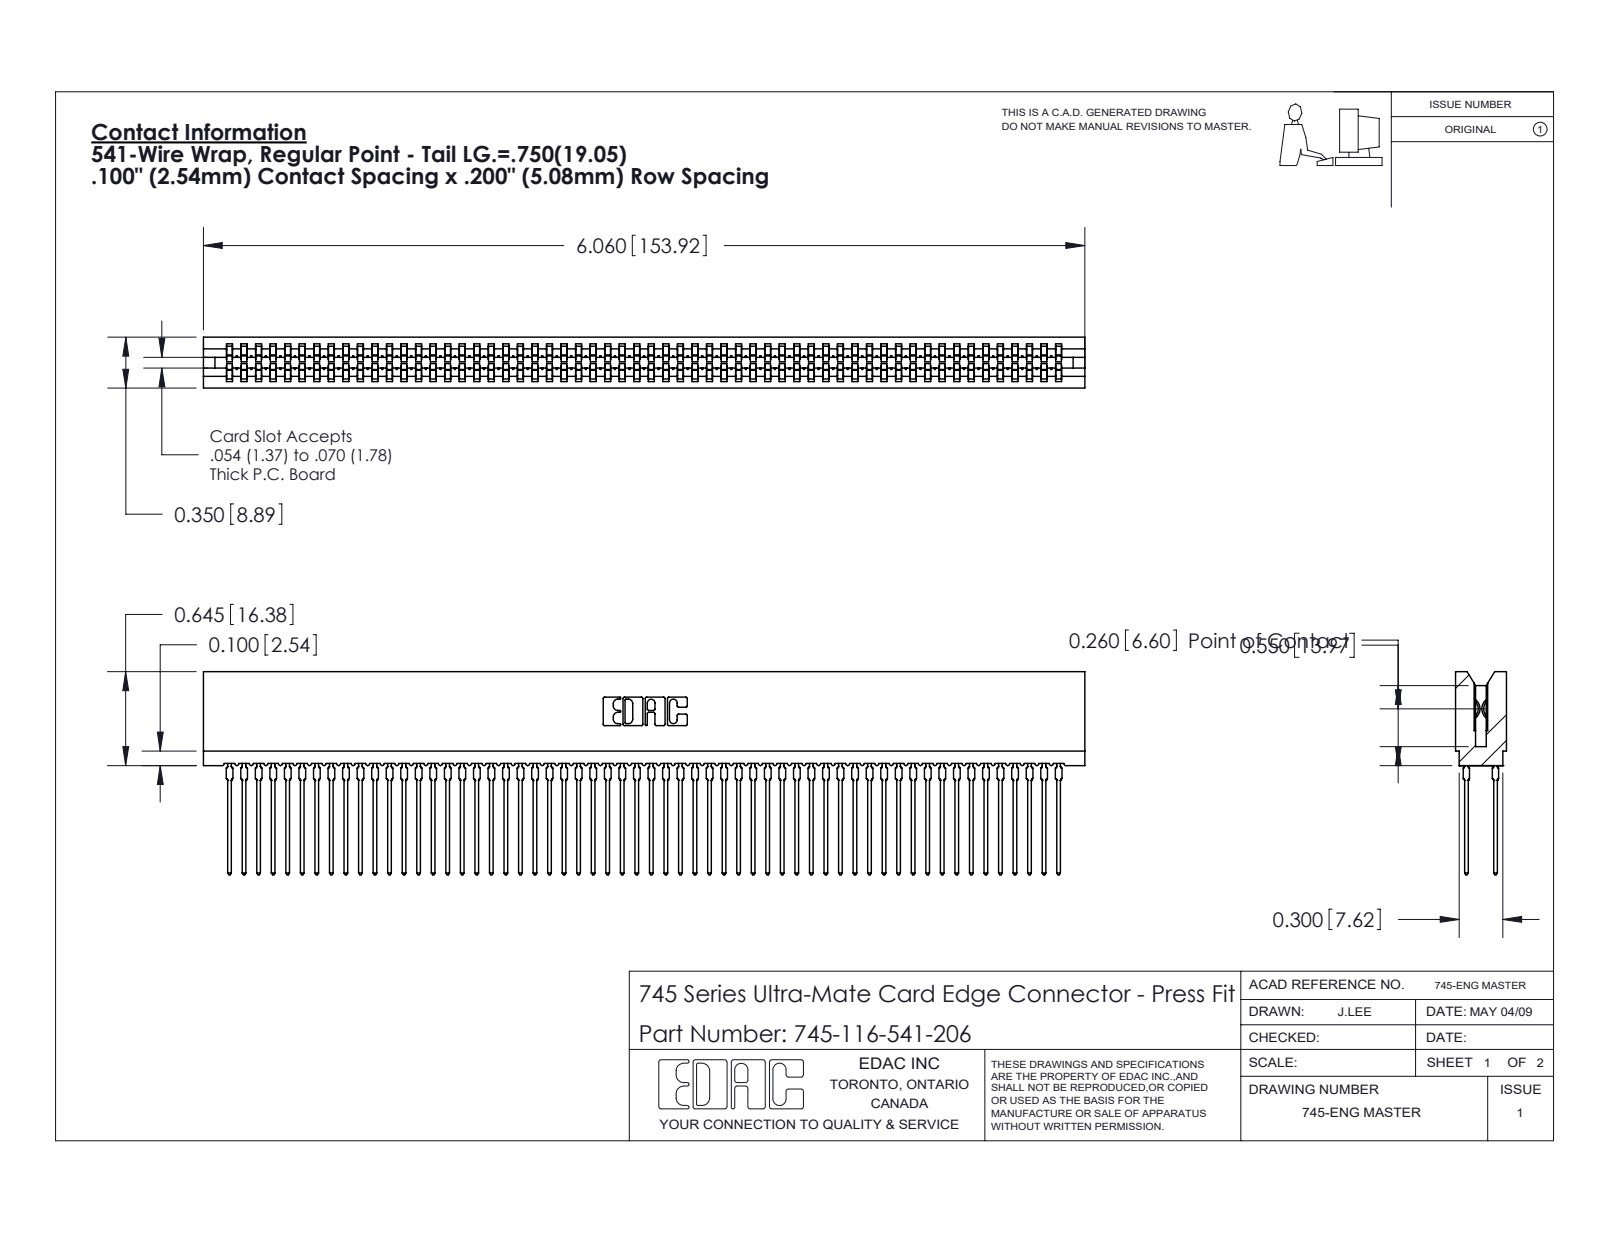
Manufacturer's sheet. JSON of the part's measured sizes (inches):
{"part_name": "745 Part_Insulator Option - 06; 745-292-001_541; 745-116-541-206", "step_written_by": "SolidWorks 2020 (CONFIG_CONTROL_DESIGN)", "units": "inches", "bodies": {"solids": 117, "faces": 10478, "planar": 5392, "cylindrical": 2070, "other": 3016}, "overall_size": [6.06, 1.396, 0.35], "volume_in3": 0.873, "surface_area_in2": 49.28, "partial_cylinders_radius": [[0.021, 232], [0.015, 116], [0.01, 22], [0.005, 8], [0.011, 8], [0.007, 6], [0.031, 6], [0.026, 3]], "face_to_face_distances": [0.063, 0.287, 0.35, 0.2, 0.087, 0.263, 0.025, 0.045, 0.305, 0.018]}
